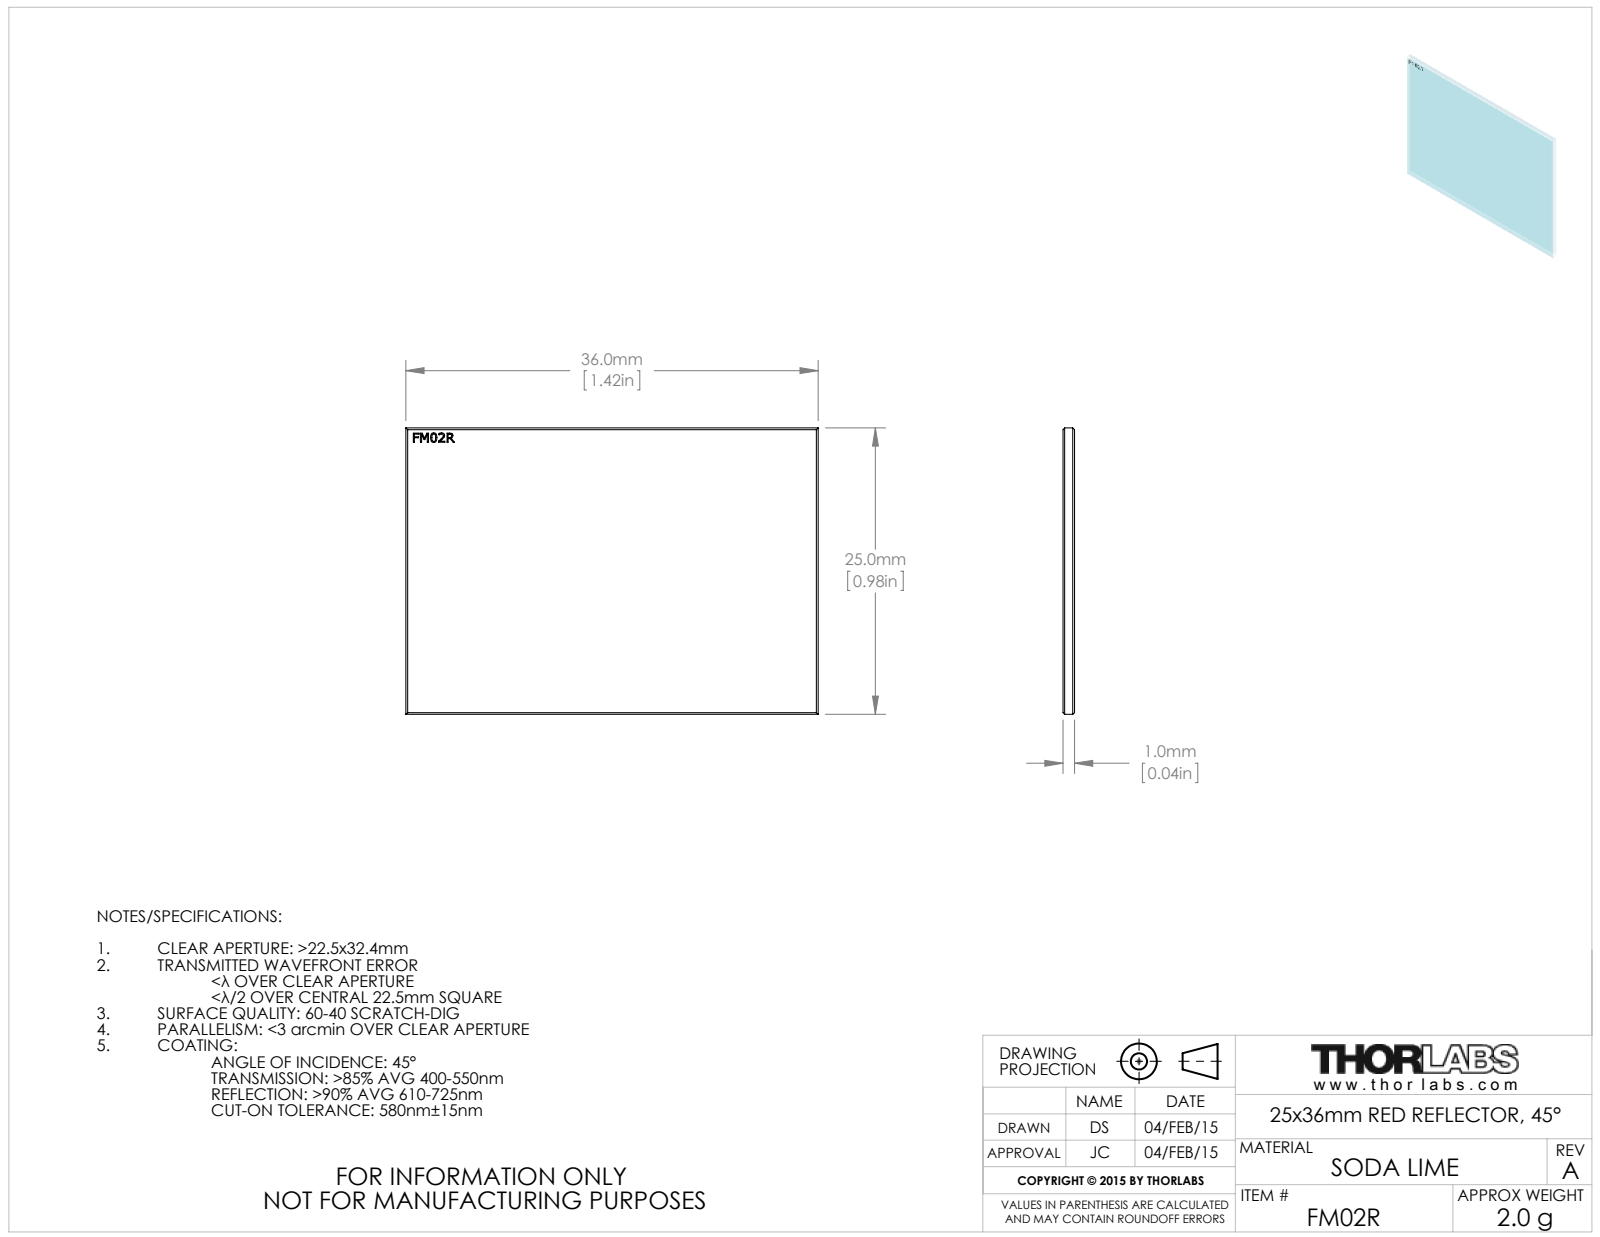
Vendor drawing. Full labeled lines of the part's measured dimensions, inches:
Part name (STEP PRODUCT): TTN034988-E0W
STEP written by: SolidWorks 2014 (CONFIG_CONTROL_DESIGN)
Units: inches
Bodies: 1 solid, 21 faces (21 planar, 0 cylindrical, 0 other)
Overall size (bounding box): 1.417 × 0.984 × 0.039
Volume: 0.055 in³ · Surface area: 2.945 in²
Main face-to-face distances: 0.039, 0.984, 1.417, 0.715, 1.021
